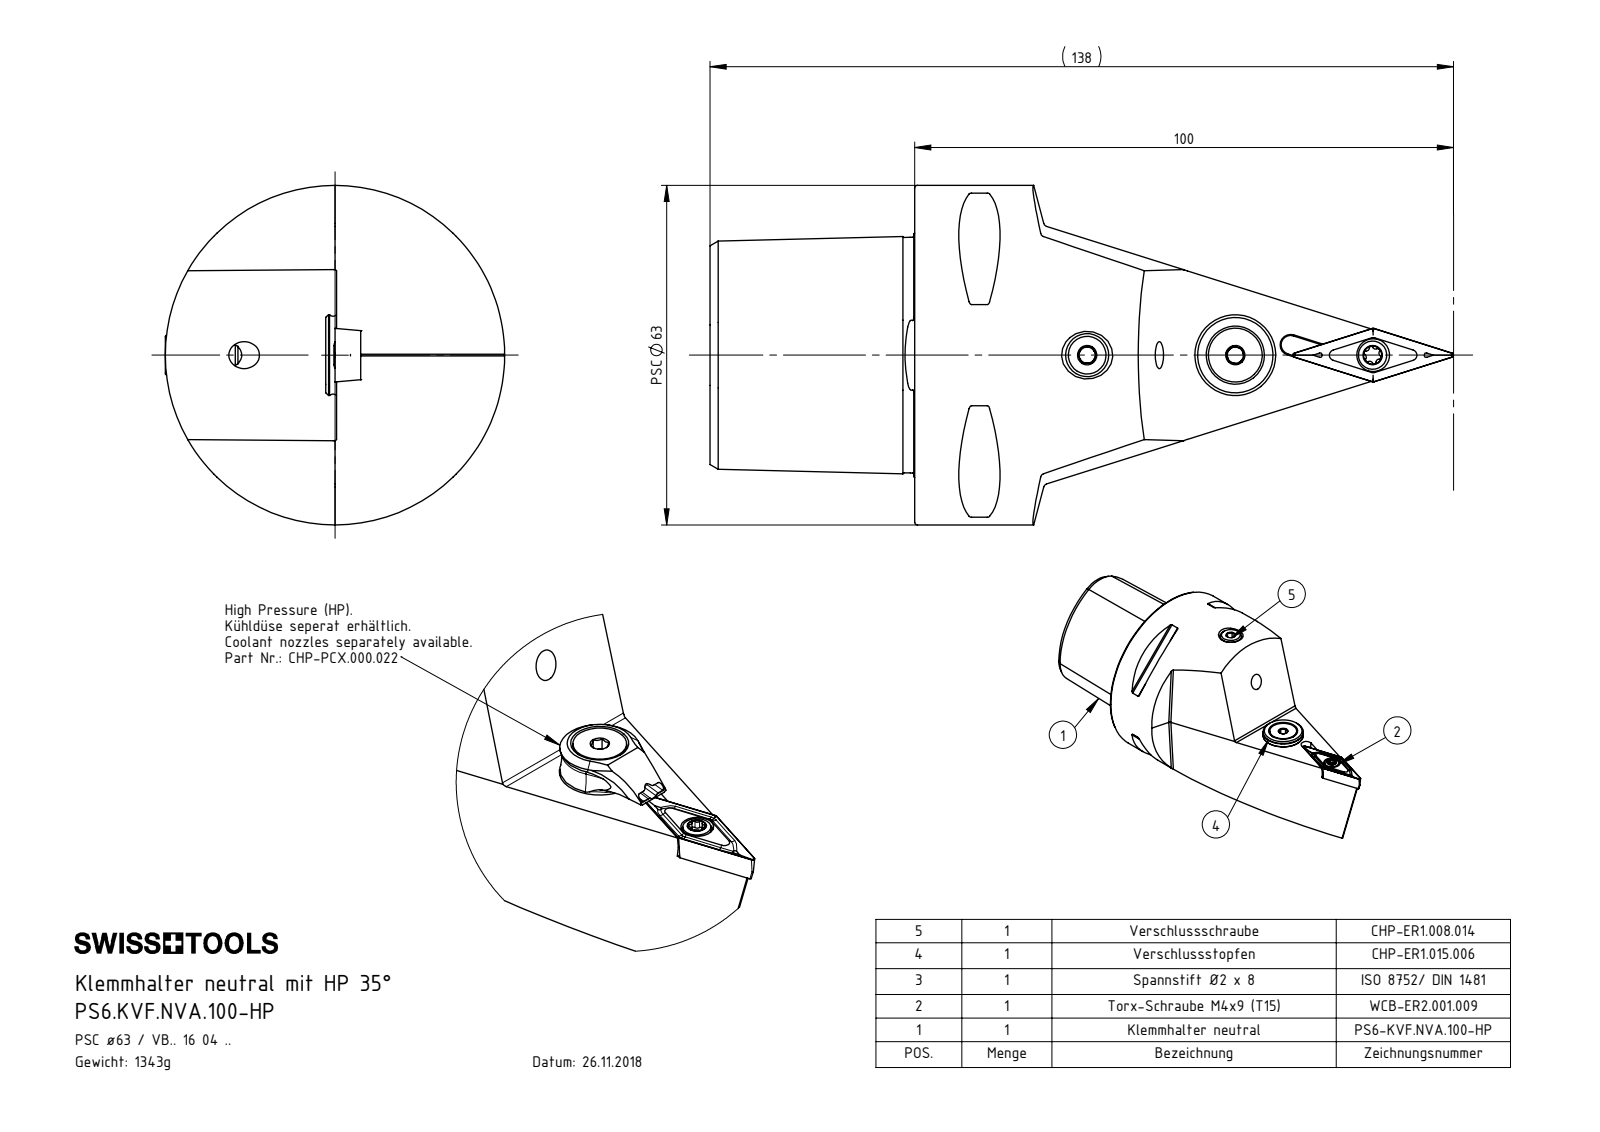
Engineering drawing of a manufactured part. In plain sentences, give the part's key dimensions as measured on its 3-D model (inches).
The part is named "WCB-ER2.001.009_A; DIN 7991 - M5x15; CHP-ER1.015.006; CHP-ER1.015.006_A (+6 more)". Its 3-D file was written by "SolidWorks 2017 (AUTOMOTIVE_DESIGN)". It is 8 solids with 379 faces: 92 planar, 101 cylindrical and 186 other. Overall it measures 5.433 by 2.48 by 2.48 inches. Its volume is 10.94 cubic inches and its surface area 50.43 square inches. Round holes: 2 of diameter 0.165, 2 of diameter 0.197, 1 of diameter 0.047, 1 of diameter 0.079, 1 of diameter 0.098, 1 of diameter 0.118, 1 of diameter 0.13, 1 of diameter 0.157, 1 of diameter 0.173, 1 of diameter 0.205, 1 of diameter 0.24, 1 of diameter 0.276. Round bosses or shafts: 1 of diameter 2.48, 1 of diameter 0.591, 1 of diameter 0.528, 1 of diameter 0.394, 1 of diameter 0.315, 1 of diameter 0.217, 1 of diameter 0.207, 1 of diameter 0.197. Partial cylindrical surfaces (rounded edges, fillets, slot ends): 8 of radius 0.02, 6 of radius 0.013, 6 of radius 0.023, 2 of radius 0.006, 2 of radius 0.236, 2 of radius 0.276, 1 of radius 0.069. The main face-to-face distances are 1.496, 0.98, 0.176, 0.177, 1.063, 0.433, 2.197, 1.488, 0.425, 0.252. The hole center spacings are 0.177, 0.63, 0.873, 0.877, 1.004, 1.007, 1.083, 1.24.
